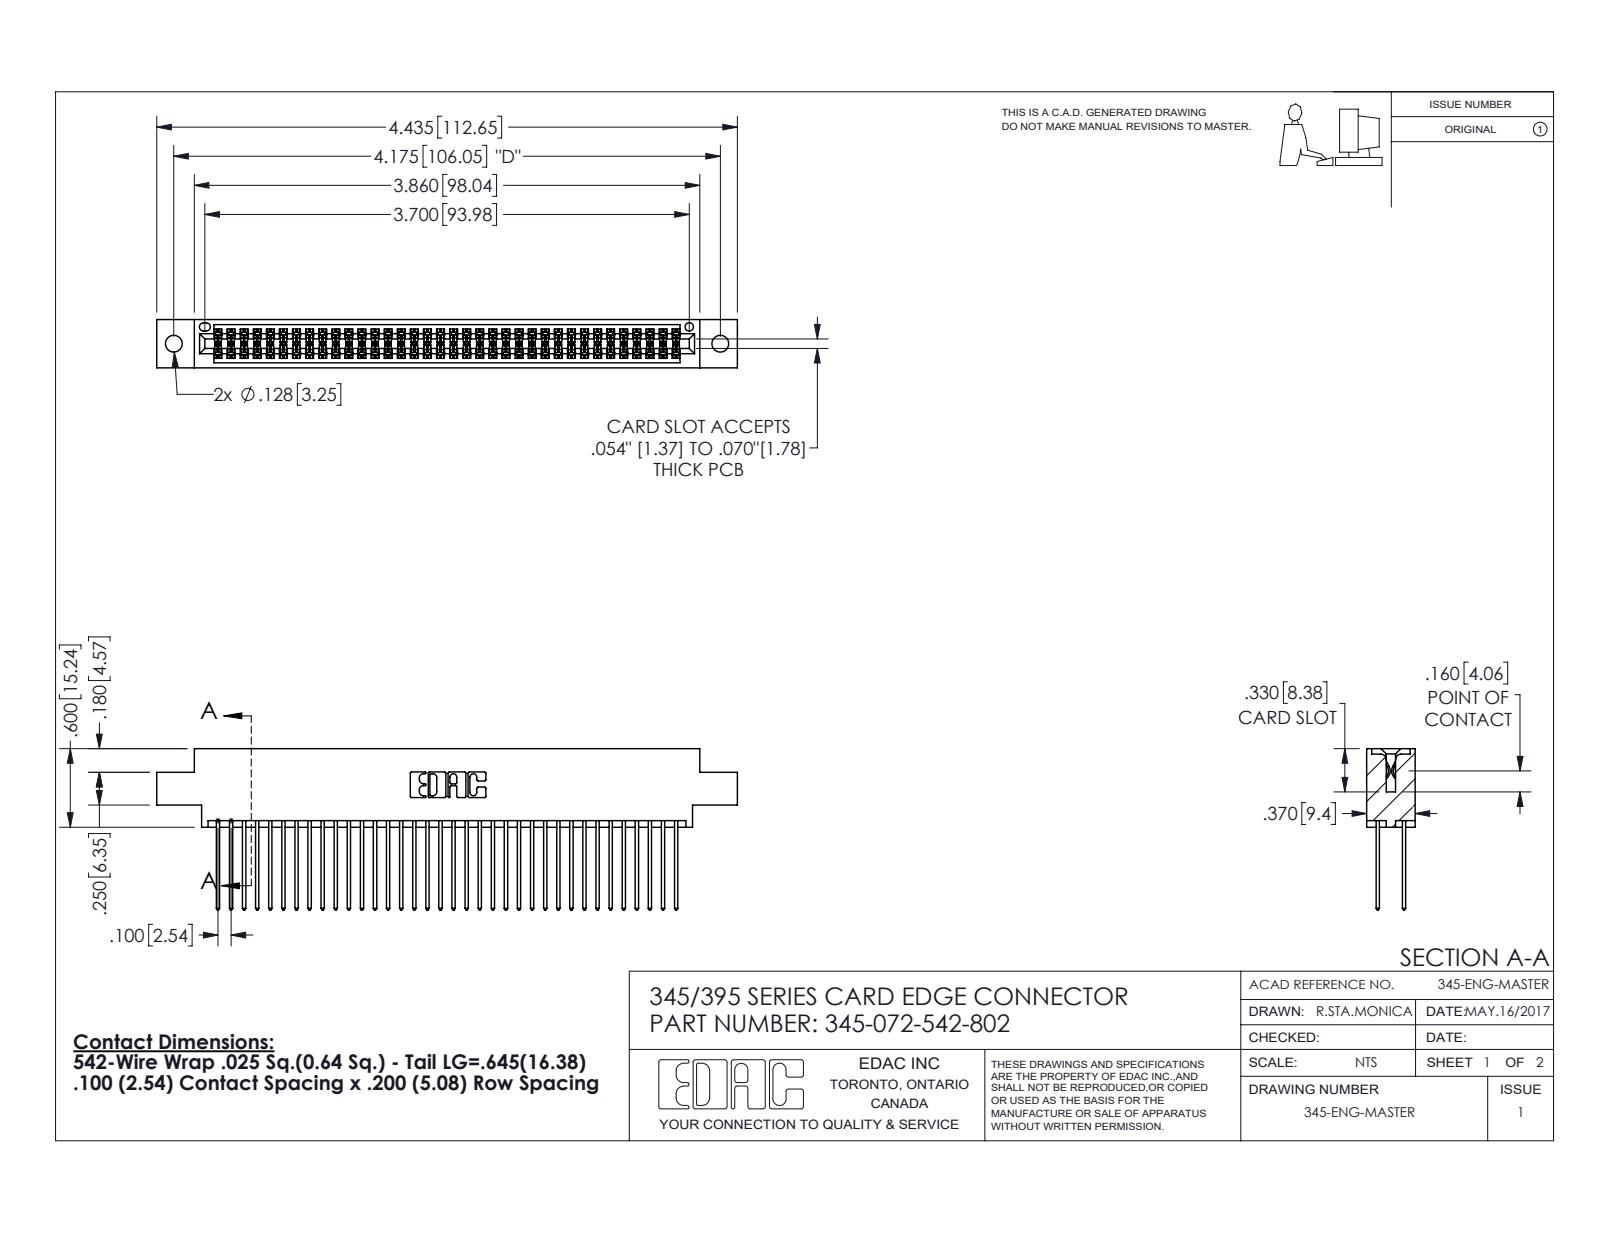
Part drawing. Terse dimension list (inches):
name: 345 Part_0.170 Offset - 0.128 Dia; 345-292-001_345-293-142; 345-072-542-802
written by: SolidWorks 2016 (CONFIG_CONTROL_DESIGN)
unit: in
bodies: 73 solids, 3730 faces (2460 planar, 1270 cylindrical, 0 other)
size: 4.435 × 1.232 × 0.37
volume: 0.676 in³; area: 27.42 in²
holes: 2× ⌀0.128, 1× ⌀0.064
rounds: 108× R0.006, 72× R0.01, 22× R0.01, 6× R0.007, 6× R0.031, 3× R0.026, 2× R0.014, 2× R0.019
face distances: 0.298, 0.072, 0.2, 0.098, 0.272, 0.025, 0.37, 0.225, 0.175, 0.149
hole spacings: 0.27, 3.939, 4.175
